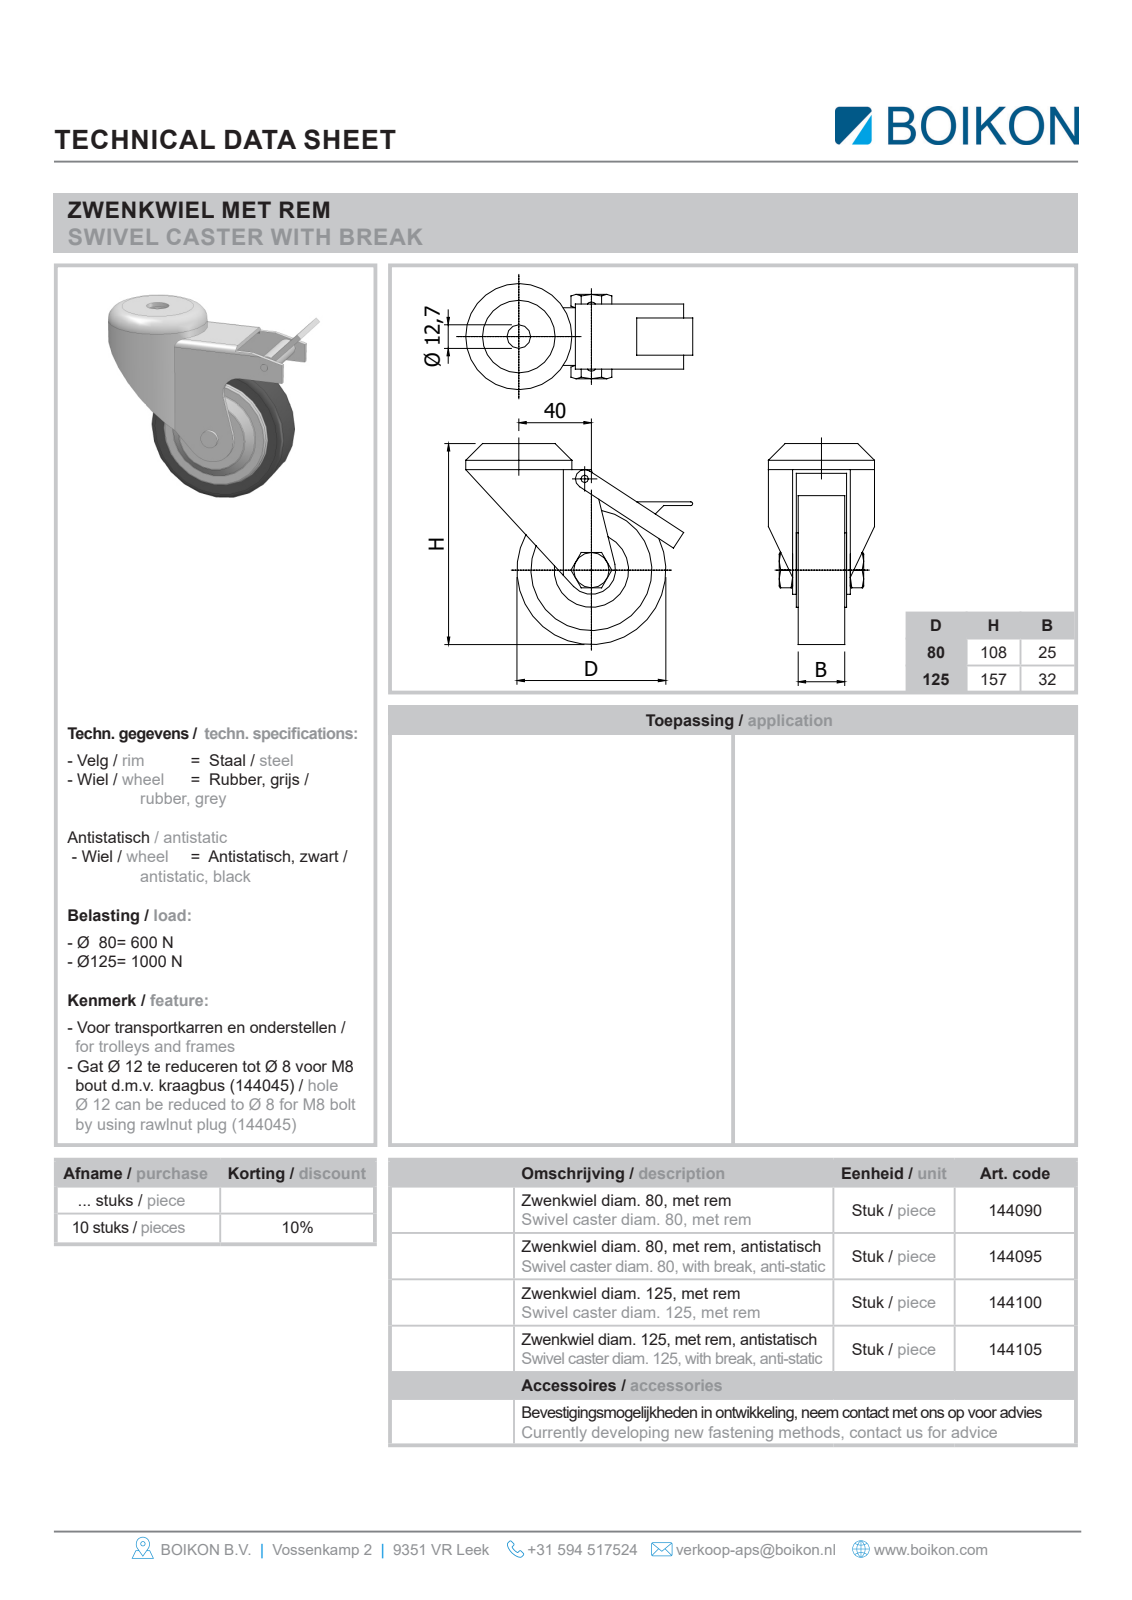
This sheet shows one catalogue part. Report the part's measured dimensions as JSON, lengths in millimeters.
{"part_name": "Root; 144090Zwenkwiel diam. 80, met remBOIKON", "step_written_by": "HiCAD 2013 1802.4 Build 509 (AUTOMOTIVE_DESIGN)", "units": "millimeters", "bodies": {"solids": 1, "faces": 71, "planar": 35, "cylindrical": 22, "other": 14}, "overall_size": [120.07, 108, 57], "volume_mm3": 189909, "surface_area_mm2": 45029, "round_holes": [[13, 1], [52, 1]], "round_bosses_or_shafts": [[10, 2], [80, 1], [62, 1], [57, 1], [4, 1]], "partial_cylinders_radius": [[1.5, 2], [4, 2], [10, 1], [14, 1]], "face_to_face_distances": [2.5, 40.5, 43, 12, 6.25, 38, 6.75, 34.25, 33.75, 27.5]}
